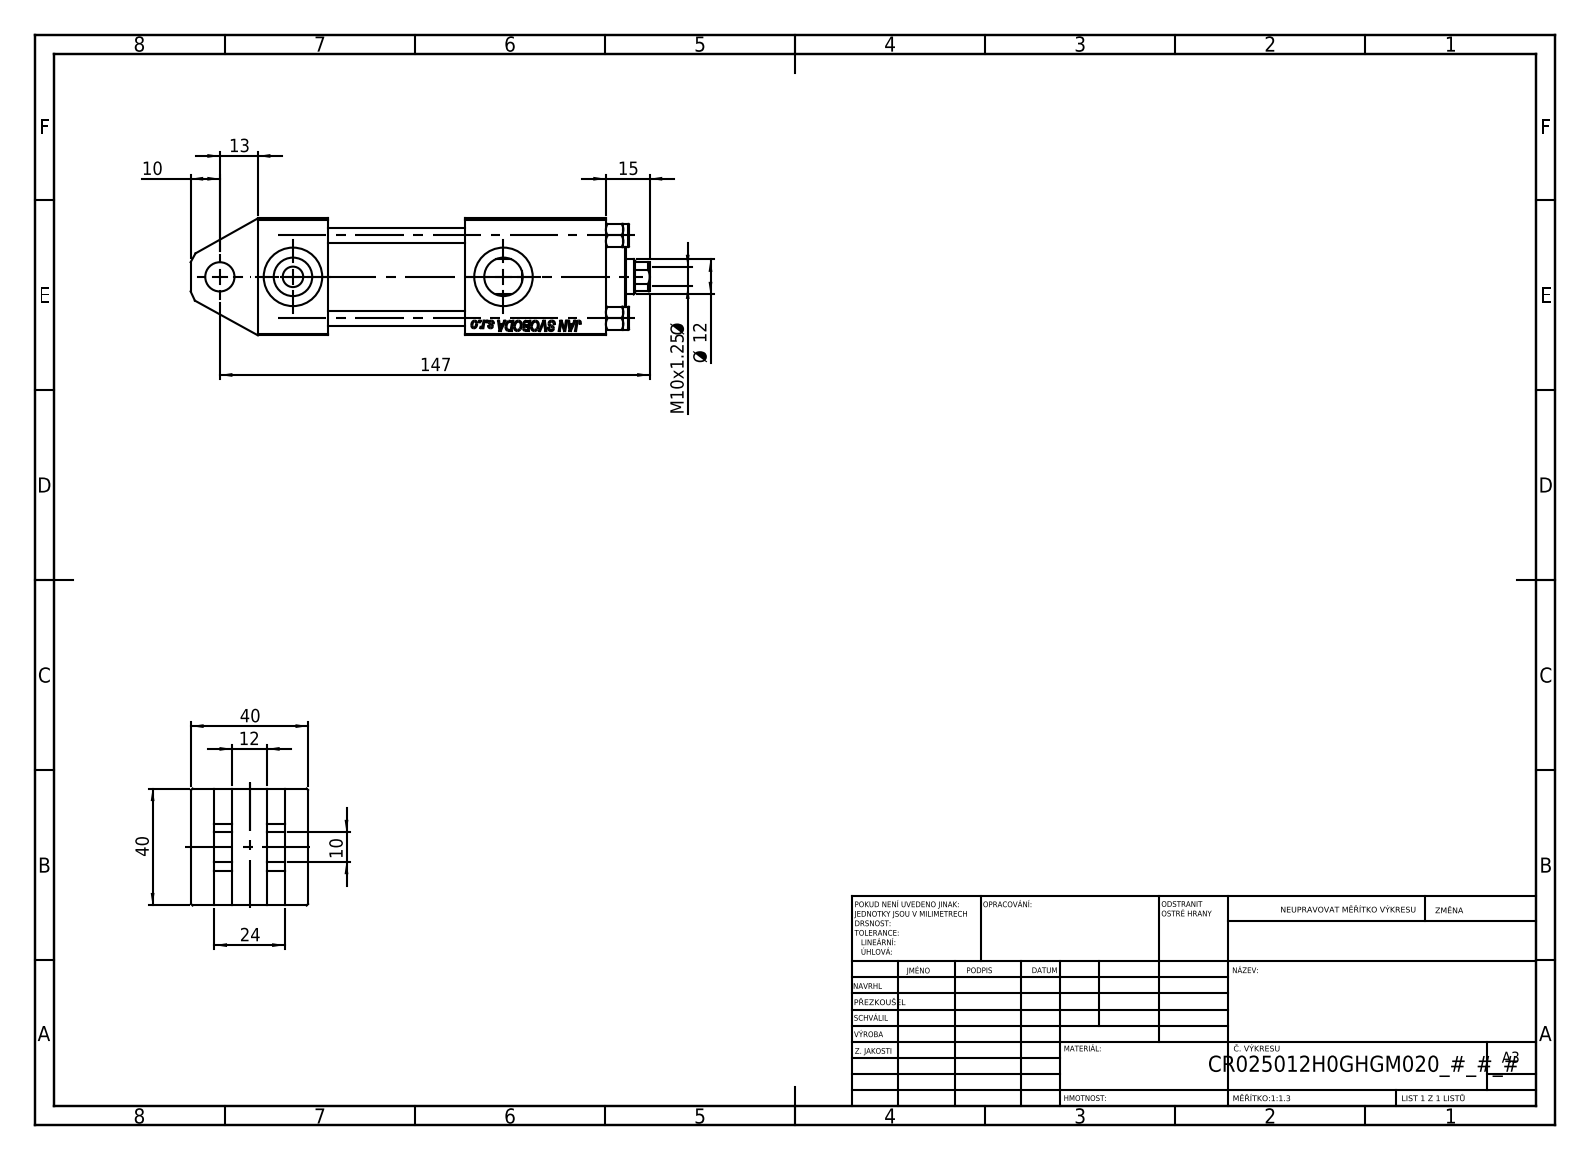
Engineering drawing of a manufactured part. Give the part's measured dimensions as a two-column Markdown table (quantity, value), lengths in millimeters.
| quantity | value |
| --- | --- |
| part name | NUT_M5_H; V215CR_TYCINKA_H; V215CR_H_Body; V215_VC_A (+1 more) |
| STEP written by | SolidWorks 2019 (CONFIG_CONTROL_DESIGN) |
| units | millimeters |
| bodies | 11 solids, 1128 faces (517 planar, 83 cylindrical, 528 other) |
| overall size | 157 × 40 × 40 |
| volume | 149 797 mm³ |
| surface area | 59 570 mm² |
| round holes (diameter × count) | 5 × 4, 20 × 3, 7 × 2, 13.16 × 2, 6.5 × 1, 10 × 1, 12 × 1, 15 × 1, 25 × 1, 30 × 1 |
| round bosses / shafts (diameter × count) | 8 × 4, 31 × 1, 24 × 1 |
| partial cylindrical surfaces (radius × count) | 5.5 × 1 |
| main face-to-face distances | 40, 24, 8, 32, 6, 14, 26, 18, 47, 119 |
| hole center spacings | 20.01, 28.3, 40.02, 25, 72, 97 |
